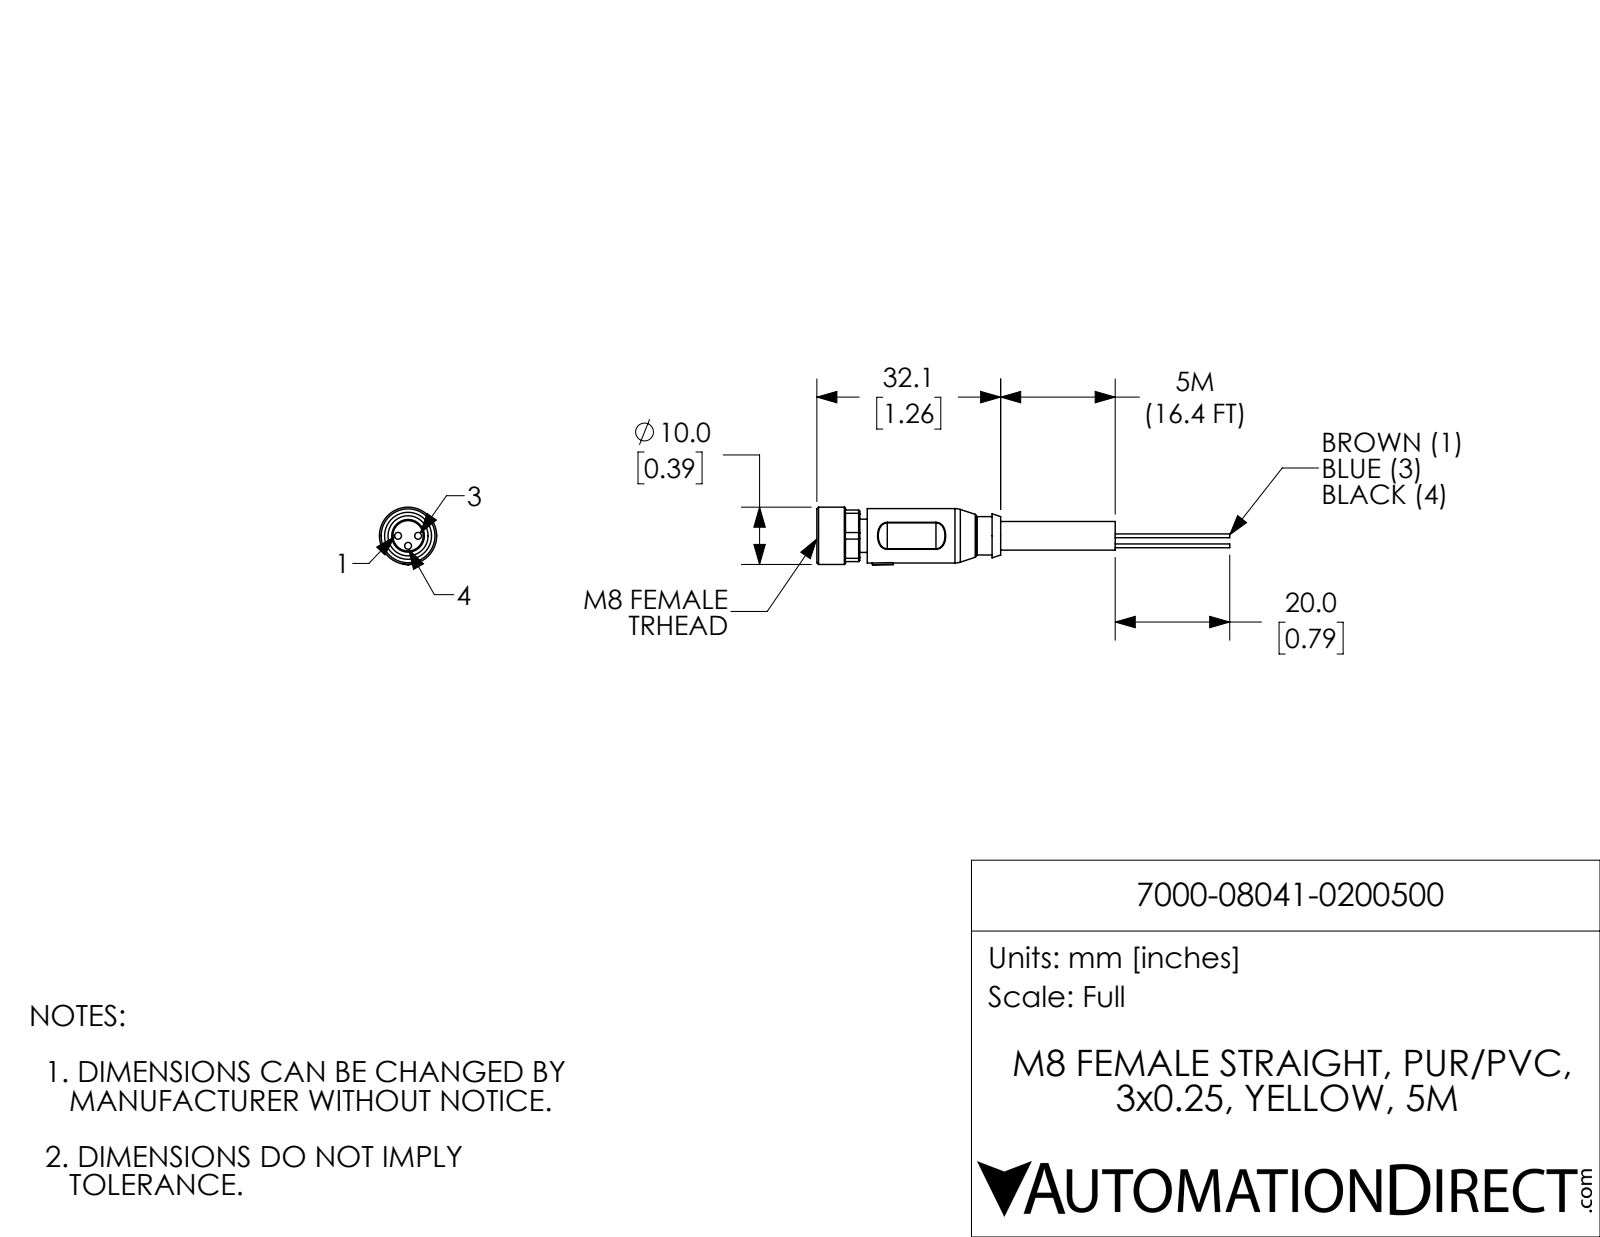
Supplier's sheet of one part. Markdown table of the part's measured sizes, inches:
| quantity | value |
| --- | --- |
| part name | 7000-08041-0200500 |
| STEP written by | SolidWorks 2017 (AUTOMOTIVE_DESIGN) |
| units | inches |
| bodies | 1 solid, 109 faces (36 planar, 42 cylindrical, 31 other) |
| overall size | 2.839 × 0.396 × 0.394 |
| volume | 0.141 in³ |
| surface area | 2.851 in² |
| round holes (diameter × count) | 0.047 × 3, 0.276 × 1 |
| round bosses / shafts (diameter × count) | 0.026 × 3, 0.394 × 1, 0.374 × 1, 0.264 × 1, 0.228 × 1, 0.224 × 1, 0.197 × 1 |
| partial cylindrical surfaces (radius × count) | 0.008 × 4, 0.098 × 4, 0.193 × 1, 0.199 × 1 |
| main face-to-face distances | 0.327, 0.051, 0.969, 0.354, 0.059, 0.028, 0.268, 0.319, 2.024, 1.756 |
| hole center spacings | 0.069, 0.097, 0.138 |
